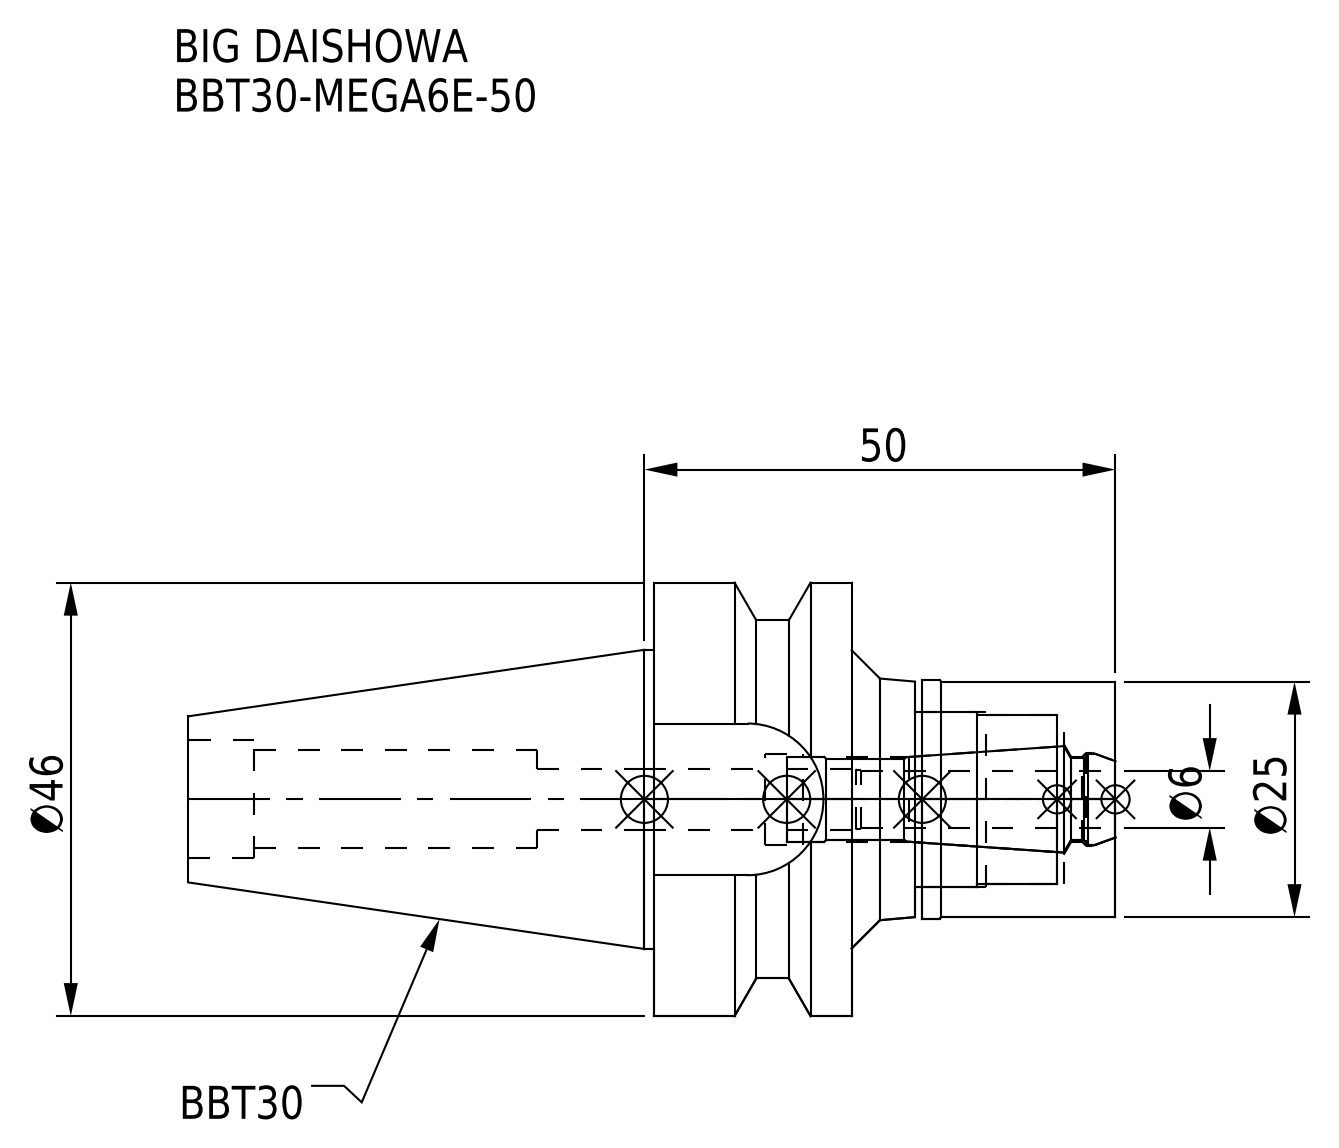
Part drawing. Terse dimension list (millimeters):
name: DXF_TEMP_ASSY_ASM_4_ASM.stp; MEN6_1.stp; BBT30-MEGA6E-50; BBT30ME06050-060_ASM.stp (+3 more)
written by: SolidWorks 2019 (CONFIG_CONTROL_DESIGN)
unit: mm
bodies: 2 solids, 78 faces (20 planar, 38 cylindrical, 20 other)
size: 98.4 × 46 × 46
volume: 60 906 mm³; area: 17 582 mm²
holes: 1× ⌀6.4, 1× ⌀9, 1× ⌀9.6, 1× ⌀9.9, 1× ⌀10.4, 1× ⌀12.5, 1× ⌀18, 1× ⌀18.5
bosses: 1× ⌀46, 1× ⌀31.75, 1× ⌀25.3, 1× ⌀25
rounds: 1× R8.05, 1× R19
face distances: 21, 28, 49, 32.6, 7.5, 20.5, 28.5, 27.7, 21.3, 0.8
